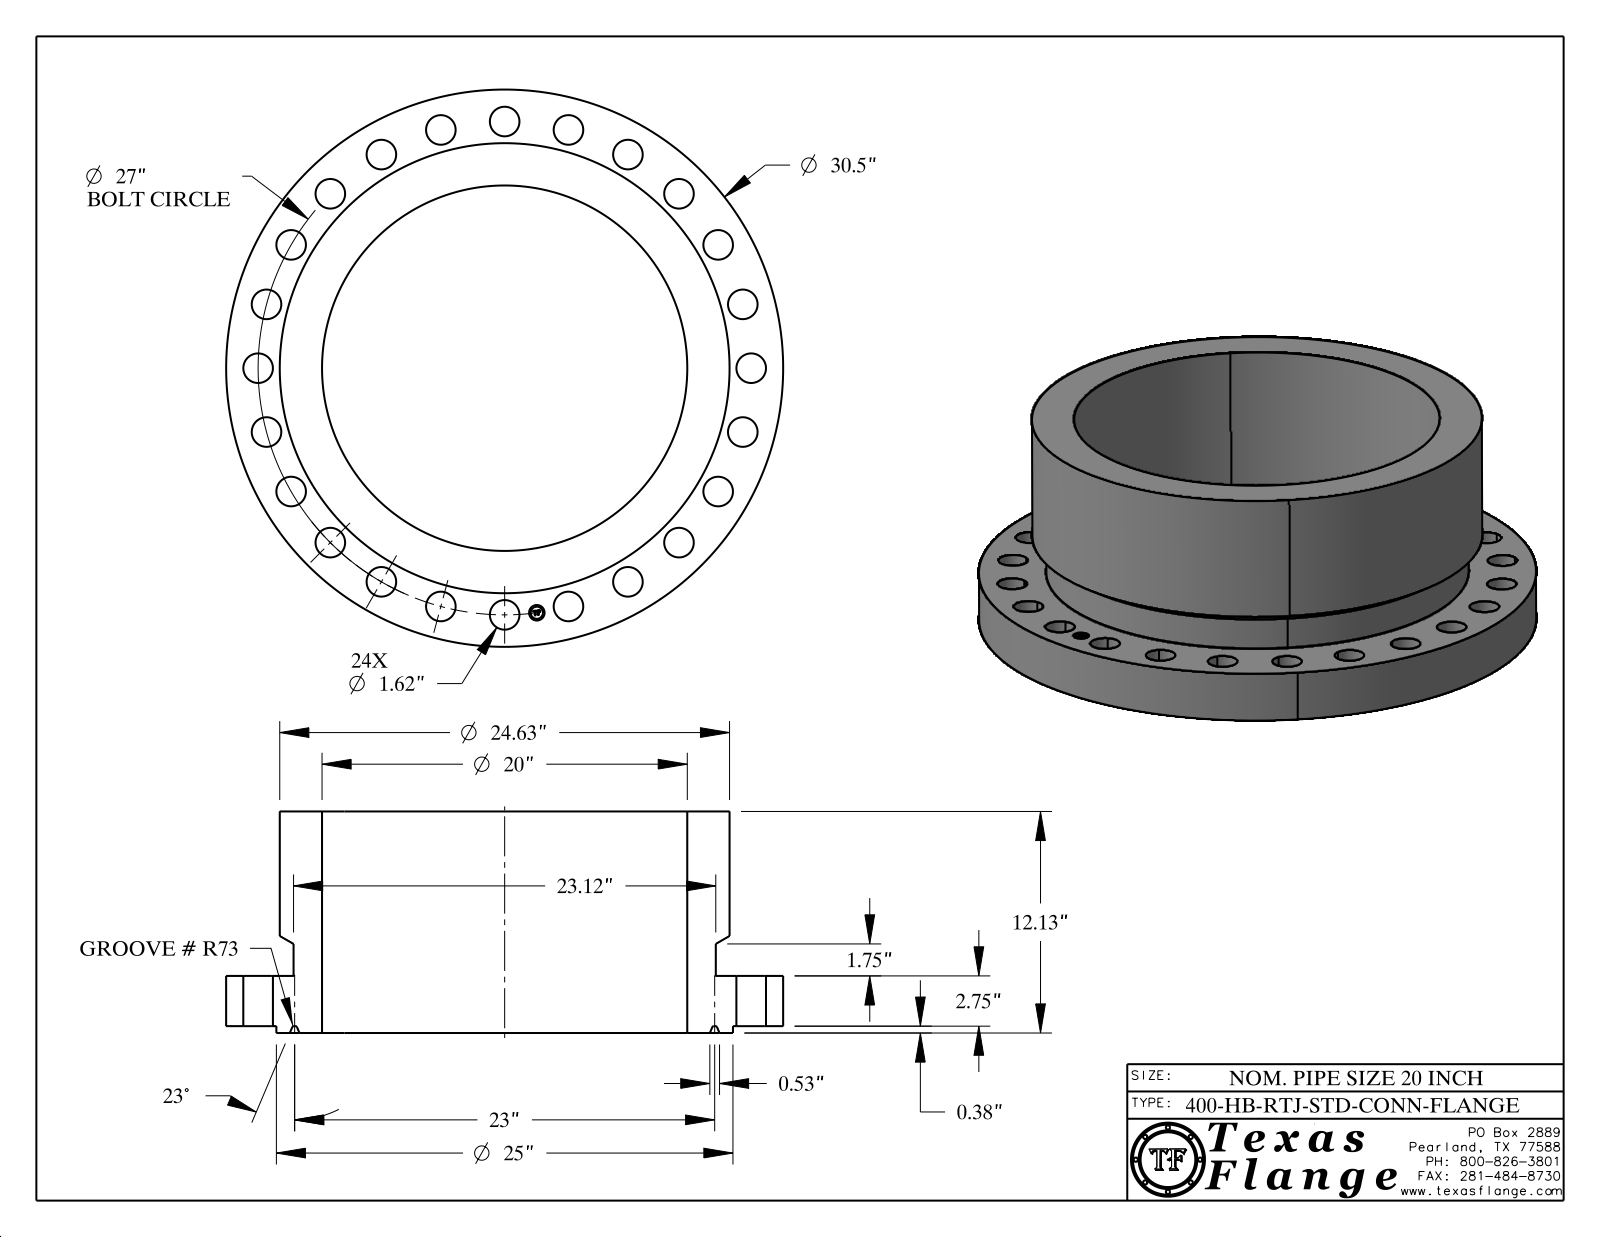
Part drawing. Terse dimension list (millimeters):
name: 20-400-HB-RTJ-STD-CONN-FLANGE
written by: CATIA V5 STEP AP214 (AUTOMOTIVE_DESIGN)
unit: mm
bodies: 1 solid, 463 faces (371 planar, 78 cylindrical, 14 other)
size: 774.7 × 774.7 × 308
volume: 39 560 000 mm³; area: 1 895 000 mm²
holes: 24× ⌀41.1, 1× ⌀21.6, 1× ⌀508
bosses: 8× ⌀1.3, 1× ⌀774.7, 1× ⌀635, 1× ⌀625.6, 1× ⌀587.2, 1× ⌀17
face distances: 69.9, 298.5, 228.6, 9.5, 79.4, 308, 79.2, 69.7, 228.7, 6.5
hole spacings: 342.9, 89.5, 177.5, 262.5, 417.5, 633.6, 679.9, 544.1
